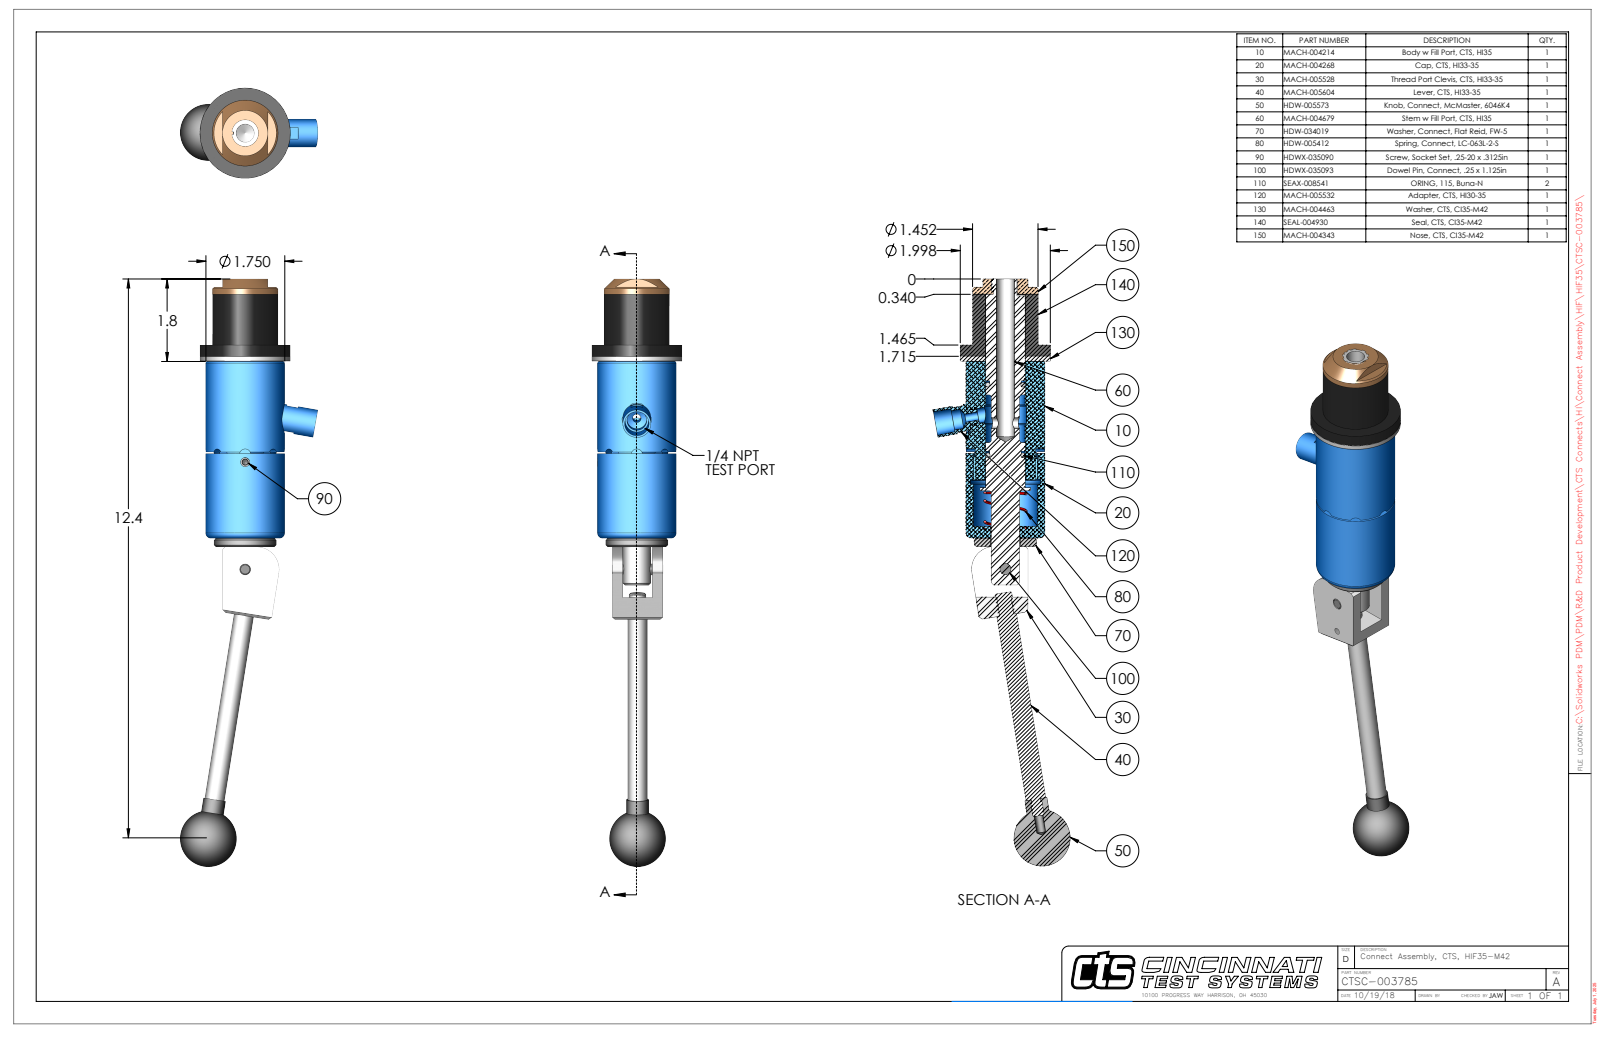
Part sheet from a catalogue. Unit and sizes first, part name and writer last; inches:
Units: inches
Overall size (bounding box): 13.02 × 3.043 × 1.998
Round holes (diameter × count): ⌀0.201 ×2, ⌀0.15 ×1, ⌀0.187 ×1, ⌀0.249 ×1, ⌀0.25 ×1, ⌀0.251 ×1, ⌀0.313 ×1, ⌀0.406 ×1, ⌀0.438 ×1, ⌀0.635 ×1, ⌀0.656 ×1, ⌀0.875 ×1
Round bosses / shafts (diameter × count): ⌀0.25 ×2, ⌀1.998 ×1, ⌀1.998 ×1, ⌀1.75 ×1, ⌀1.452 ×1, ⌀1.38 ×1, ⌀0.869 ×1, ⌀0.625 ×1
Partial cylindrical surfaces — rounded edges, fillets, slot ends (radius × count): R0.125 ×4, R0.029 ×2, R0.166 ×1, R0.249 ×1, R0.33 ×1, R0.5 ×1, R0.695 ×1, R0.815 ×1
Main face-to-face distances: 1.375, 5.405, 4.03, 1.485, 0.11, 3.92, 1.12, 1.49, 0.115, 3.915
Hole centre spacings: 0.74, 2.376, 3.116
Volume: 15 in³ · Surface area: 95.95 in²
Bodies: 9 solids, 285 faces (104 planar, 119 cylindrical, 62 other)
Part name (STEP PRODUCT): CTSC-003785
STEP written by: SolidWorks 2023 (AUTOMOTIVE_DESIGN)
